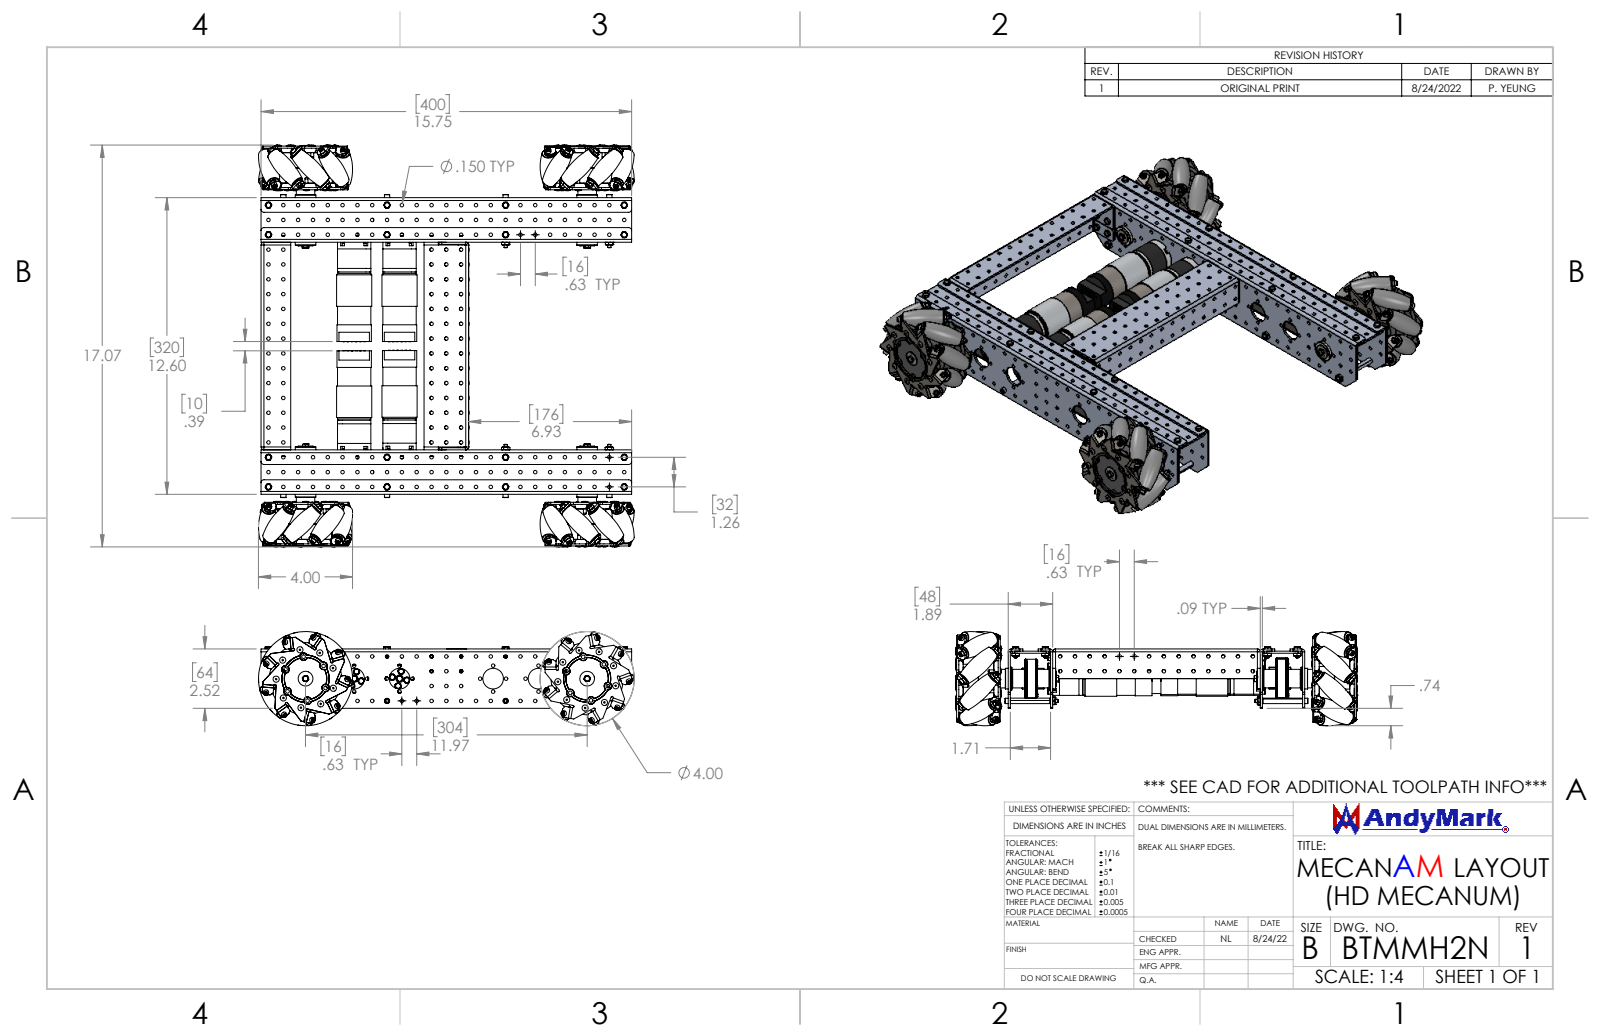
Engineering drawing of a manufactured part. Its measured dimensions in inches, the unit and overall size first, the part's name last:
Units: inches
Overall size (bounding box): 17.065 × 15.969 × 4
Round holes (diameter × count): ⌀0.15 ×344, ⌀0.135 ×173, ⌀0.116 ×120, ⌀0.063 ×72, ⌀0.135 ×56, ⌀0.125 ×47, ⌀0.123 ×36, ⌀0.187 ×36, ⌀0.098 ×30, ⌀0.111 ×28, ⌀0.191 ×28, ⌀0.157 ×24
Round bosses / shafts (diameter × count): ⌀0.287 ×72, ⌀0.262 ×72, ⌀0.125 ×72, ⌀0.217 ×59, ⌀0.118 ×59, ⌀0.138 ×42, ⌀0.187 ×30, ⌀0.15 ×26
Partial cylindrical surfaces — rounded edges, fillets, slot ends (radius × count): R0.01 ×640, R0.012 ×384, R0.017 ×384, R0.017 ×384, R0.054 ×384, R0.069 ×384, R0.089 ×384, R0.112 ×384
Main face-to-face distances: 0.09, 1.8, 10.709, 0.09, 1.89, 8.909, 1.709, 10.619, 10.799, 12.508
Hole centre spacings: 0.63, 1.26, 1.89, 3.15, 1.409, 1.992, 2.52, 3.78
Volume: 99.86 in³ · Surface area: 2 010 in²
Bodies: 520 solids, 51552 faces (8196 planar, 19252 cylindrical, 24104 other)
Part name (STEP PRODUCT): am-3104 NeveRest Motor; am-1363 Aluminum 125 Rivet_Compressed (incomplete; SHCS M3 x 16mm; NR Orbital 2 Stage Gearbox (+8 more)
STEP written by: SolidWorks 2022 (AUTOMOTIVE_DESIGN)
